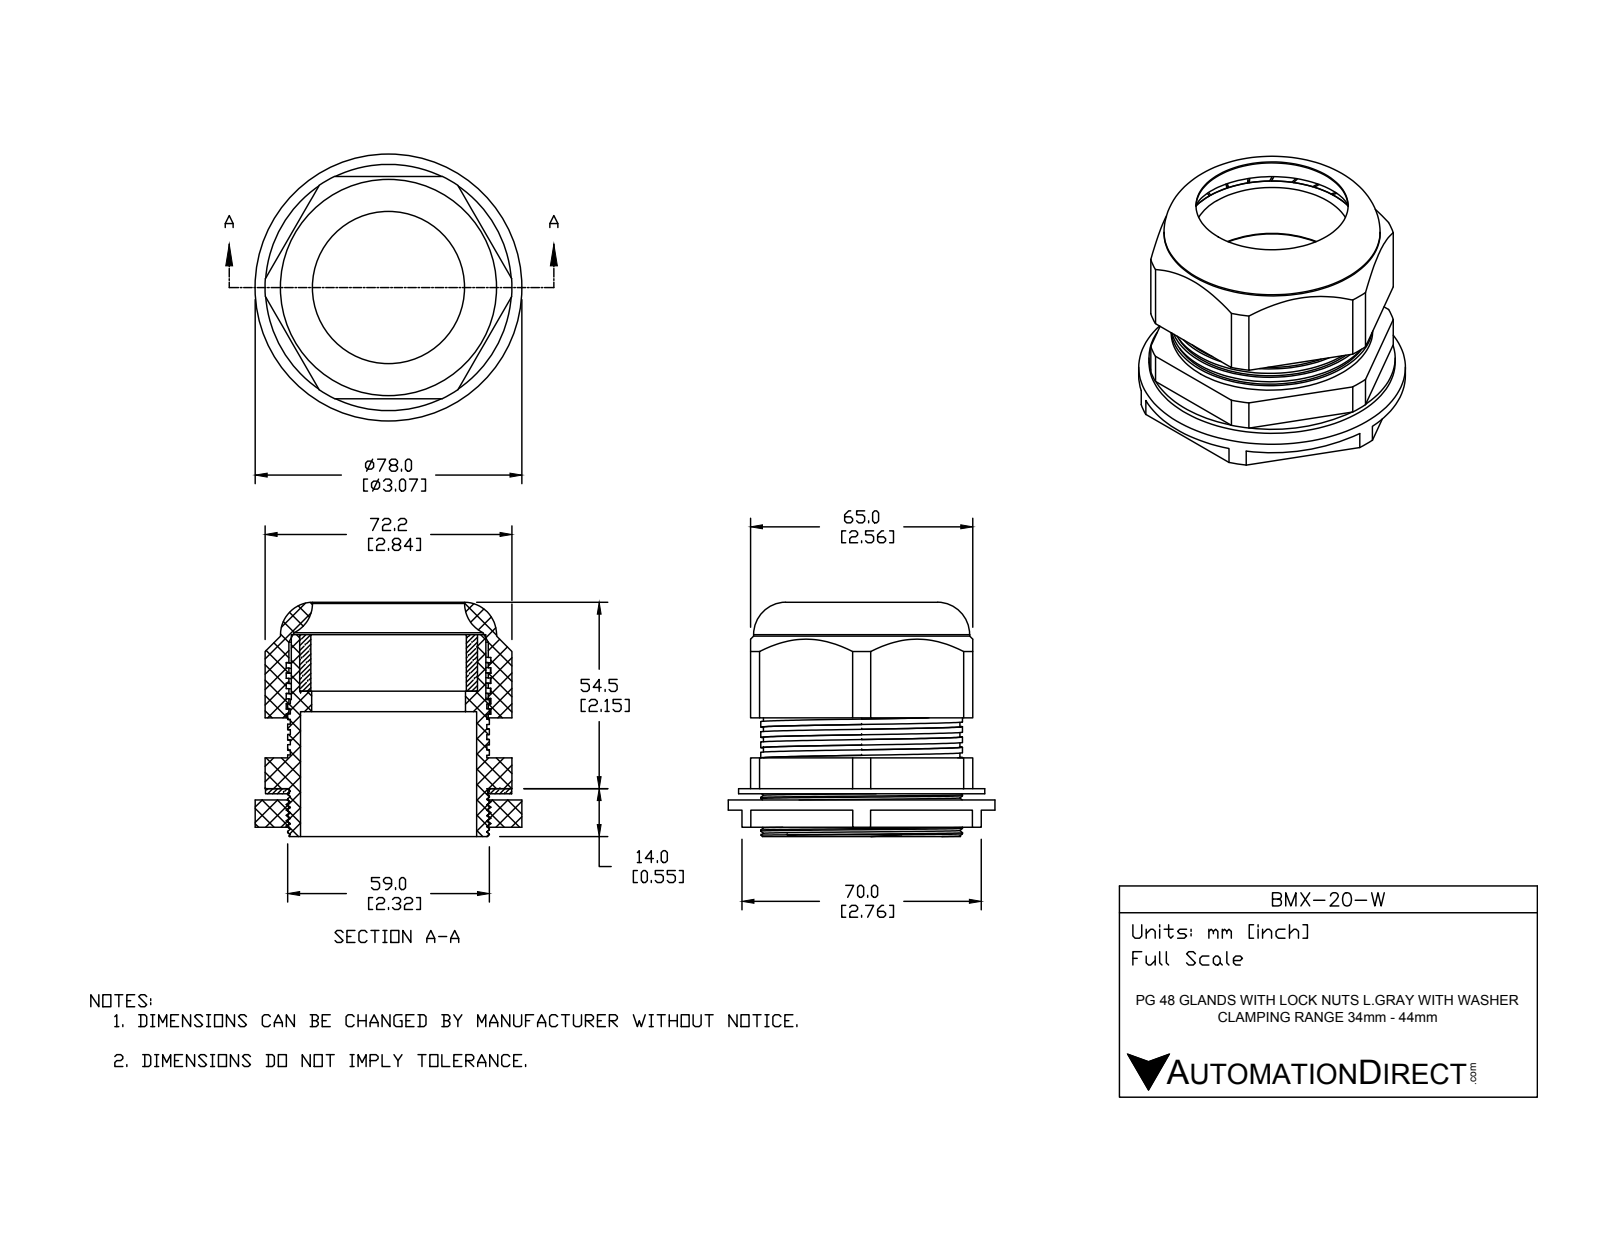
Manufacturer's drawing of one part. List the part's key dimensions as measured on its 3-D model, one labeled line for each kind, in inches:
Part name (STEP PRODUCT): BMX-20-W
STEP written by: SolidWorks 2015 (CONFIG_CONTROL_DESIGN)
Units: inches
Bodies: 5 solids, 300 faces (139 planar, 140 cylindrical, 21 other)
Overall size (bounding box): 3.071 × 3.071 × 2.697
Volume: 5.921 in³ · Surface area: 98.78 in²
Round holes (diameter × count): ⌀1.752 ×1, ⌀1.772 ×1, ⌀1.791 ×1, ⌀2.047 ×1, ⌀2.283 ×1, ⌀2.296 ×1
Round bosses / shafts (diameter × count): ⌀3.071 ×1, ⌀2.835 ×1, ⌀2.488 ×1, ⌀2.323 ×1, ⌀2.24 ×1, ⌀2.028 ×1
Partial cylindrical surfaces — rounded edges, fillets, slot ends (radius × count): R1.421 ×1
Main face-to-face distances: 2.559, 0.13, 0.071, 0.315, 0.445, 0.386, 0.059, 0.945, 0.098, 0.02
